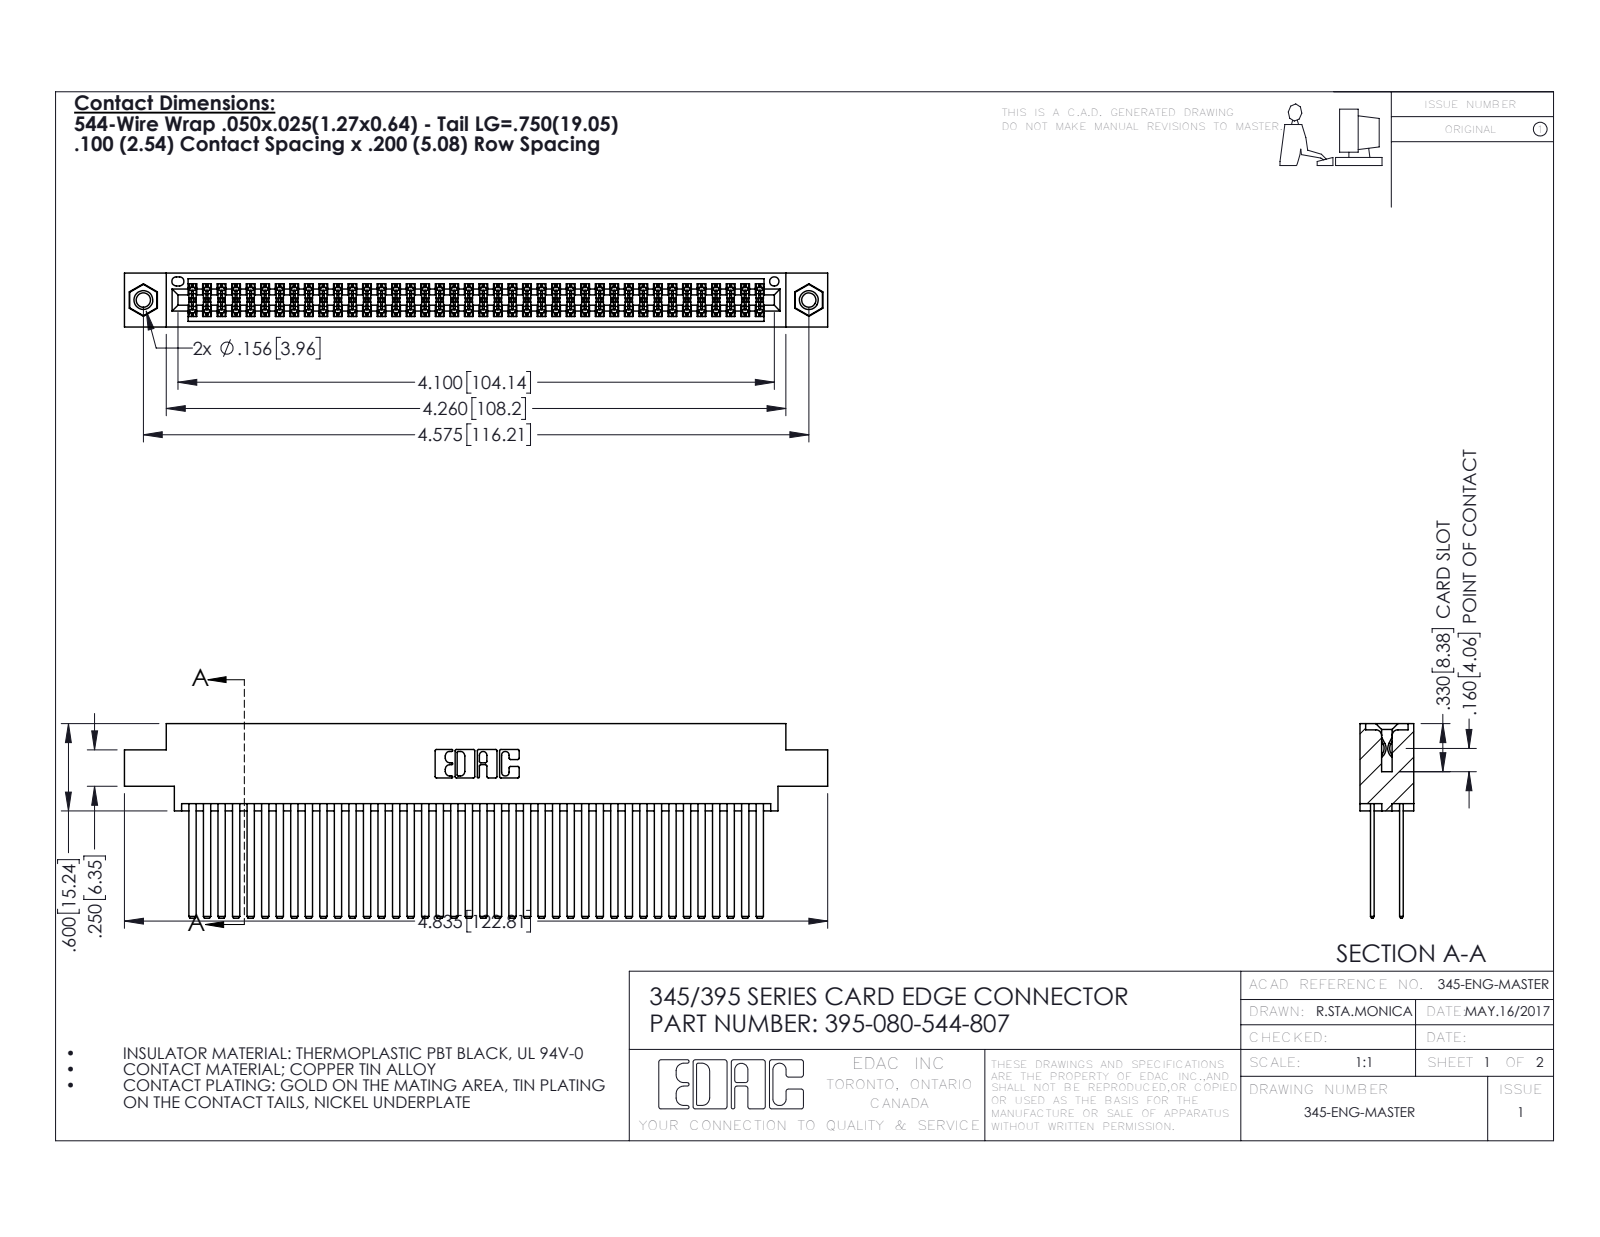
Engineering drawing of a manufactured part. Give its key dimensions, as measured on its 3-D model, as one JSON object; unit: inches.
{"part_name": "345-250-001_345-250-005-103; 345-292-001_345-293-144; 395-080-544-807; 345 Part_0.170 Offset - 0.156 Dia-TI", "step_written_by": "SolidWorks 2016 (CONFIG_CONTROL_DESIGN)", "units": "inches", "bodies": {"solids": 83, "faces": 3710, "planar": 2436, "cylindrical": 1258, "other": 16}, "overall_size": [4.835, 1.337, 0.37], "volume_in3": 0.788, "surface_area_in2": 34.87, "round_holes": [[0.098, 2], [0.125, 2], [0.156, 2], [0.064, 1]], "round_bosses_or_shafts": [[0.155, 2]], "partial_cylinders_radius": [[0.006, 120], [0.01, 22], [0.007, 6], [0.031, 6], [0.026, 3], [0.014, 2], [0.019, 2], [0.022, 2]], "face_to_face_distances": [0.2, 0.025, 0.072, 0.098, 0.272, 0.298, 0.225, 0.175, 0.37, 0.15], "hole_center_spacings": [0.27, 4.339, 4.575]}
